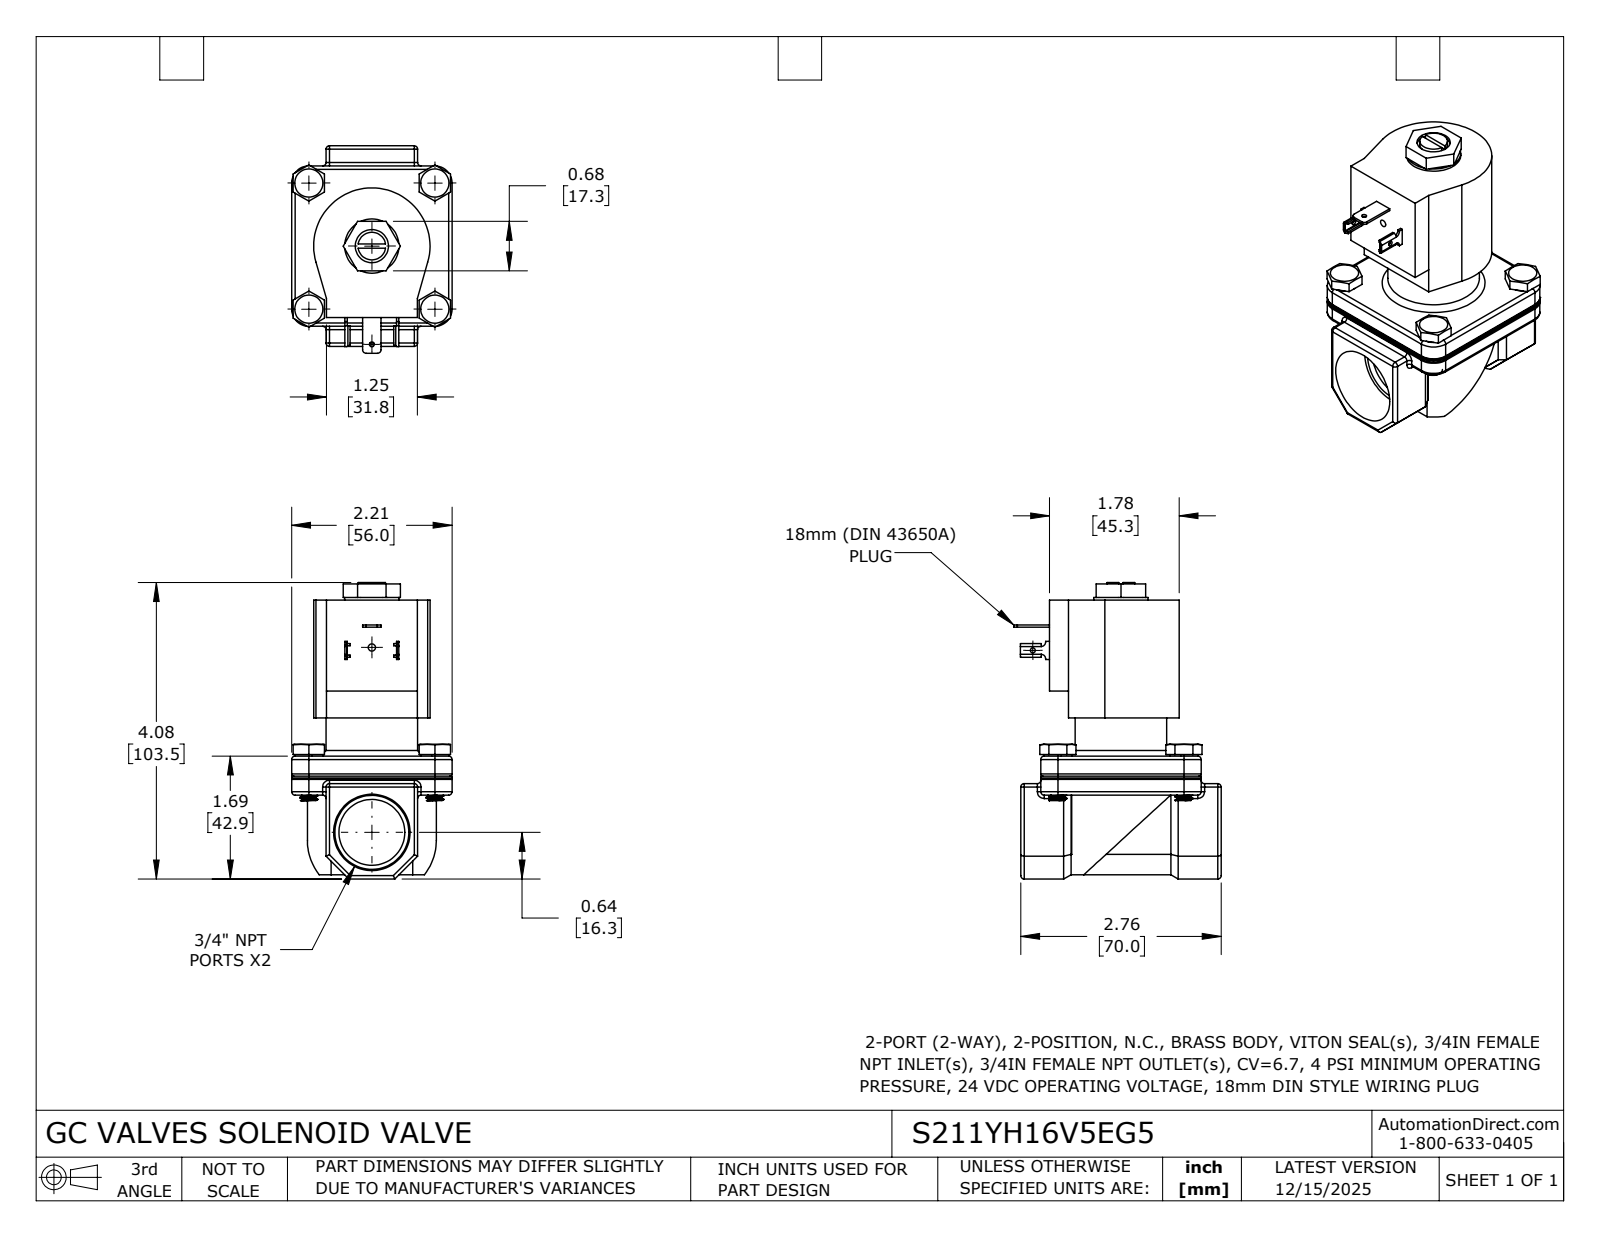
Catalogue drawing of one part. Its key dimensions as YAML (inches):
part_name: "S211YH16V5EG5"
step_written_by: "SolidWorks 2024 (CONFIG_CONTROL_DESIGN)"
units: inches
bodies: {solids: 3, faces: 348, planar: 168, cylindrical: 120, other: 60}
overall_size: [4.075, 2.851, 2.205]
volume: 9.987
surface_area: 44.97
round_holes:
  - {diameter: 0.066, count: 1}
  - {diameter: 0.067, count: 1}
  - {diameter: 0.1, count: 1}
  - {diameter: 0.456, count: 1}
  - {diameter: 0.906, count: 1}
round_bosses_or_shafts:
  - {diameter: 0.388, count: 4}
  - {diameter: 0.244, count: 4}
  - {diameter: 1.26, count: 1}
  - {diameter: 0.746, count: 1}
  - {diameter: 0.38, count: 1}
partial_cylinders:
  - {radius: 0.047, count: 34}
  - {radius: 0.006, count: 4}
  - {radius: 0.031, count: 4}
  - {radius: 0.041, count: 4}
  - {radius: 0.234, count: 4}
  - {radius: 0.236, count: 4}
  - {radius: 0.05, count: 2}
  - {radius: 0.06, count: 2}
face_to_face_distances: [0.059, 2.143, 0.472, 1.732, 0.537, 2.68, 2.205, 0.523, 1.094, 1.631]
hole_center_spacings: [1.35, 2.541]
